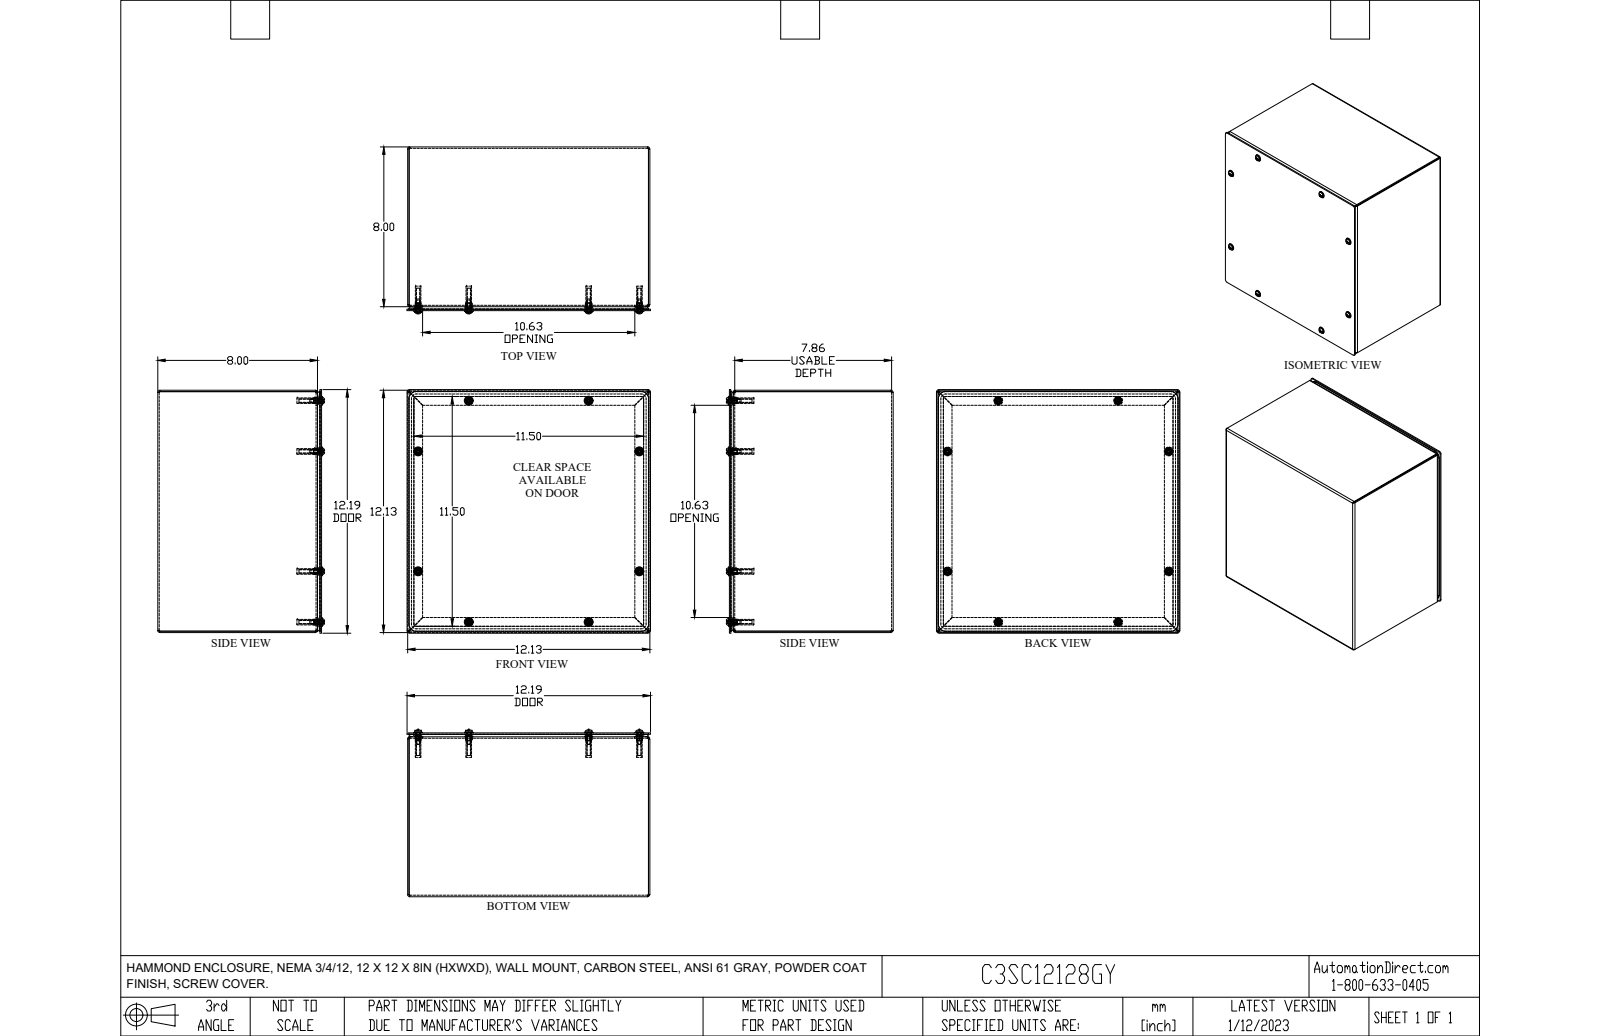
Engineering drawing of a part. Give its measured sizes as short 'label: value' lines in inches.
name: C3SC12128GY
written by: SolidWorks 2021 (AUTOMOTIVE_DESIGN)
unit: in
bodies: 27 solids, 780 faces (480 planar, 152 cylindrical, 148 other)
size: 12.188 × 12.188 × 8.347
volume: 51.28 in³; area: 1 494 in²
holes: 8× ⌀0.159, 8× ⌀0.16, 8× ⌀0.25
bosses: 8× ⌀0.44, 8× ⌀0.39, 8× ⌀0.24, 8× ⌀0.19, 8× ⌀0.148, 4× ⌀0.275, 4× ⌀0.275
rounds: 8× R0.04, 8× R0.11, 8× R0.125, 8× R0.16, 4× R0.126, 4× R0.374
face distances: 0.07, 12.13, 12.06, 0.07, 11.99, 12.06, 0.072, 8.127, 8.055, 8.197
hole spacings: 8.906, 3.589, 6, 11.075, 12.074, 12.596
